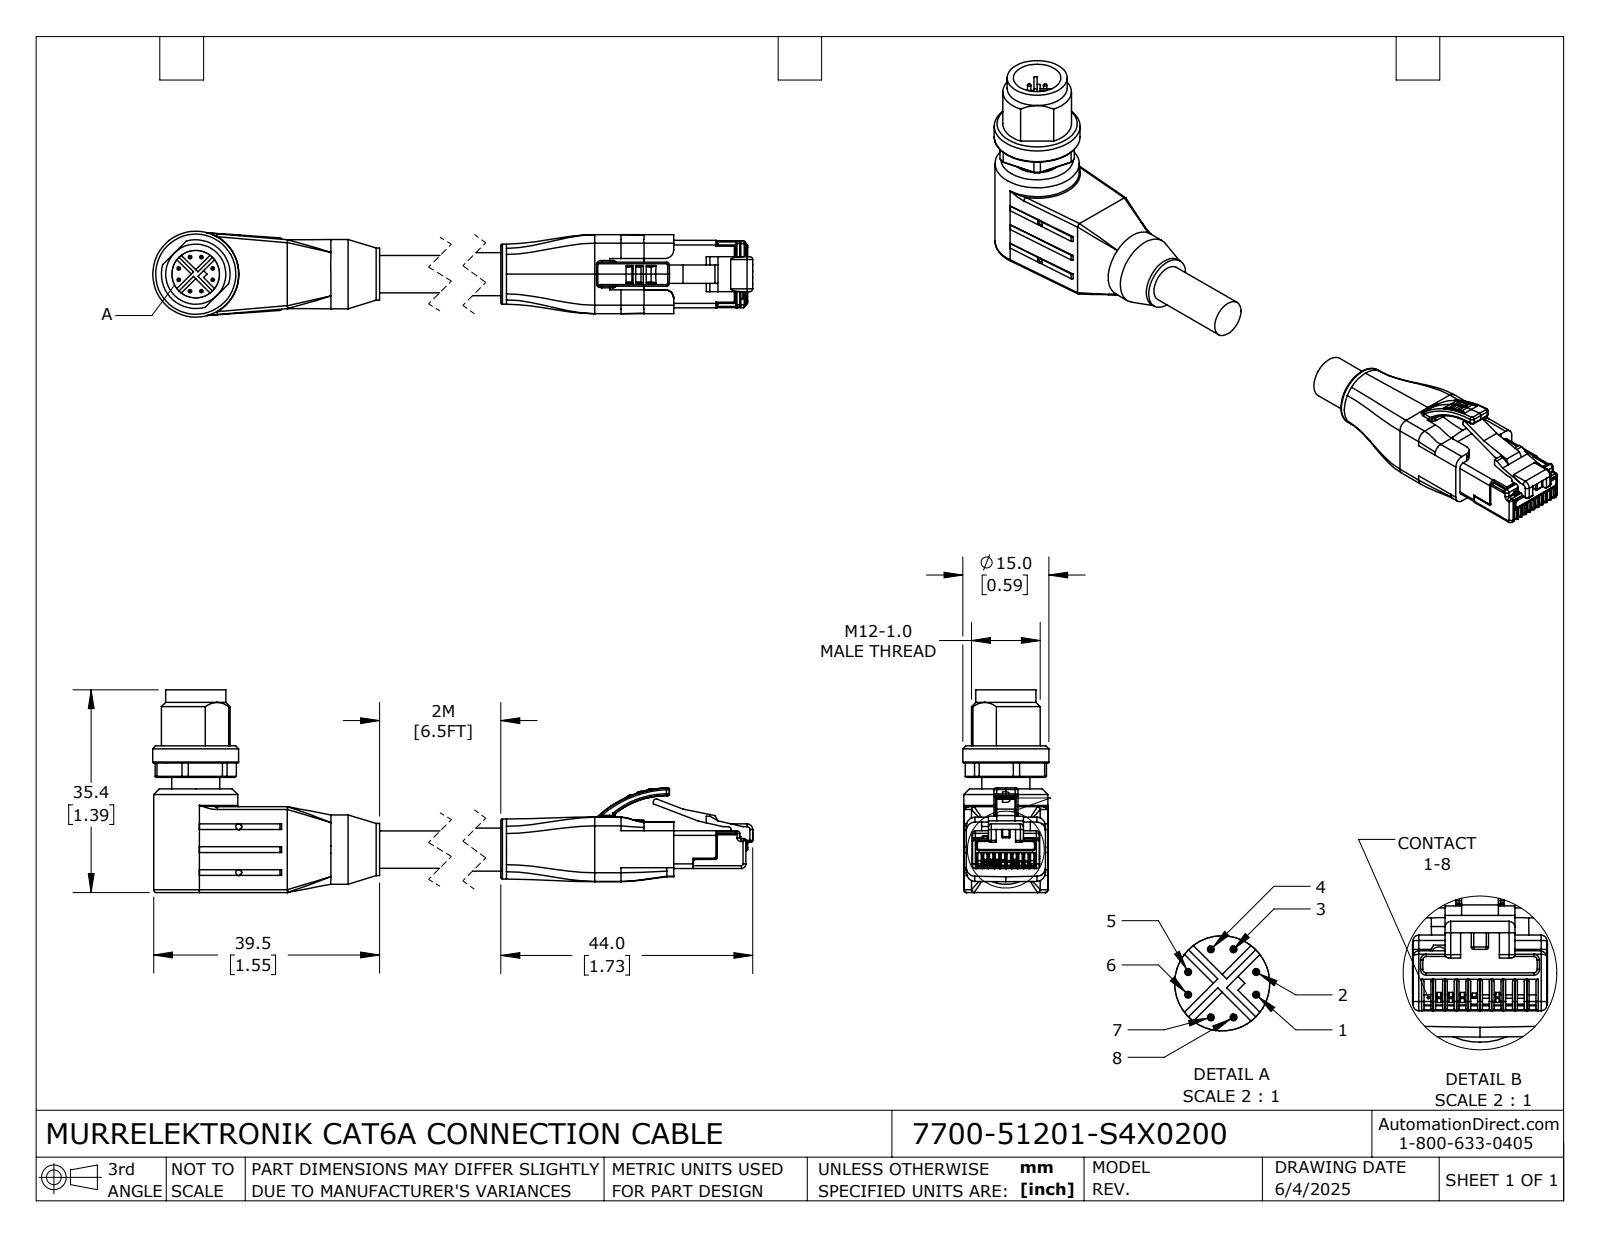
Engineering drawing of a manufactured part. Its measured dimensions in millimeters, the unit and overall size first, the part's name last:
Units: millimetres
Overall size (bounding box): 131.6 × 35.4 × 15
Round holes (diameter × count): ⌀1.05 ×4, ⌀4.8 ×1, ⌀8.3 ×1
Round bosses / shafts (diameter × count): ⌀0.6 ×8, ⌀10.5 ×2, ⌀15 ×1, ⌀14.7 ×1, ⌀12.1 ×1, ⌀9.1 ×1, ⌀8.4 ×1, ⌀7.5 ×1
Partial cylindrical surfaces — rounded edges, fillets, slot ends (radius × count): R0.2 ×61, R0.5 ×29, R0.3 ×16, R1.5 ×9, R0.8 ×5, R0.54 ×2, R5 ×2, R0.13 ×1
Main face-to-face distances: 10.8, 4.2, 15, 13.8, 5.1, 4.7, 20.1, 9.3, 18.1, 5.8
Hole centre spacings: 8
Volume: 14 317 mm³ · Surface area: 6 560 mm²
Bodies: 2 solids, 822 faces (394 planar, 249 cylindrical, 179 other)
Part name (STEP PRODUCT): 7700-51201-S4X0200_RJ45; 7700-51201-S4X0200; 7700-51201-S4X0200_MALE
STEP written by: SolidWorks 2024 (CONFIG_CONTROL_DESIGN)
